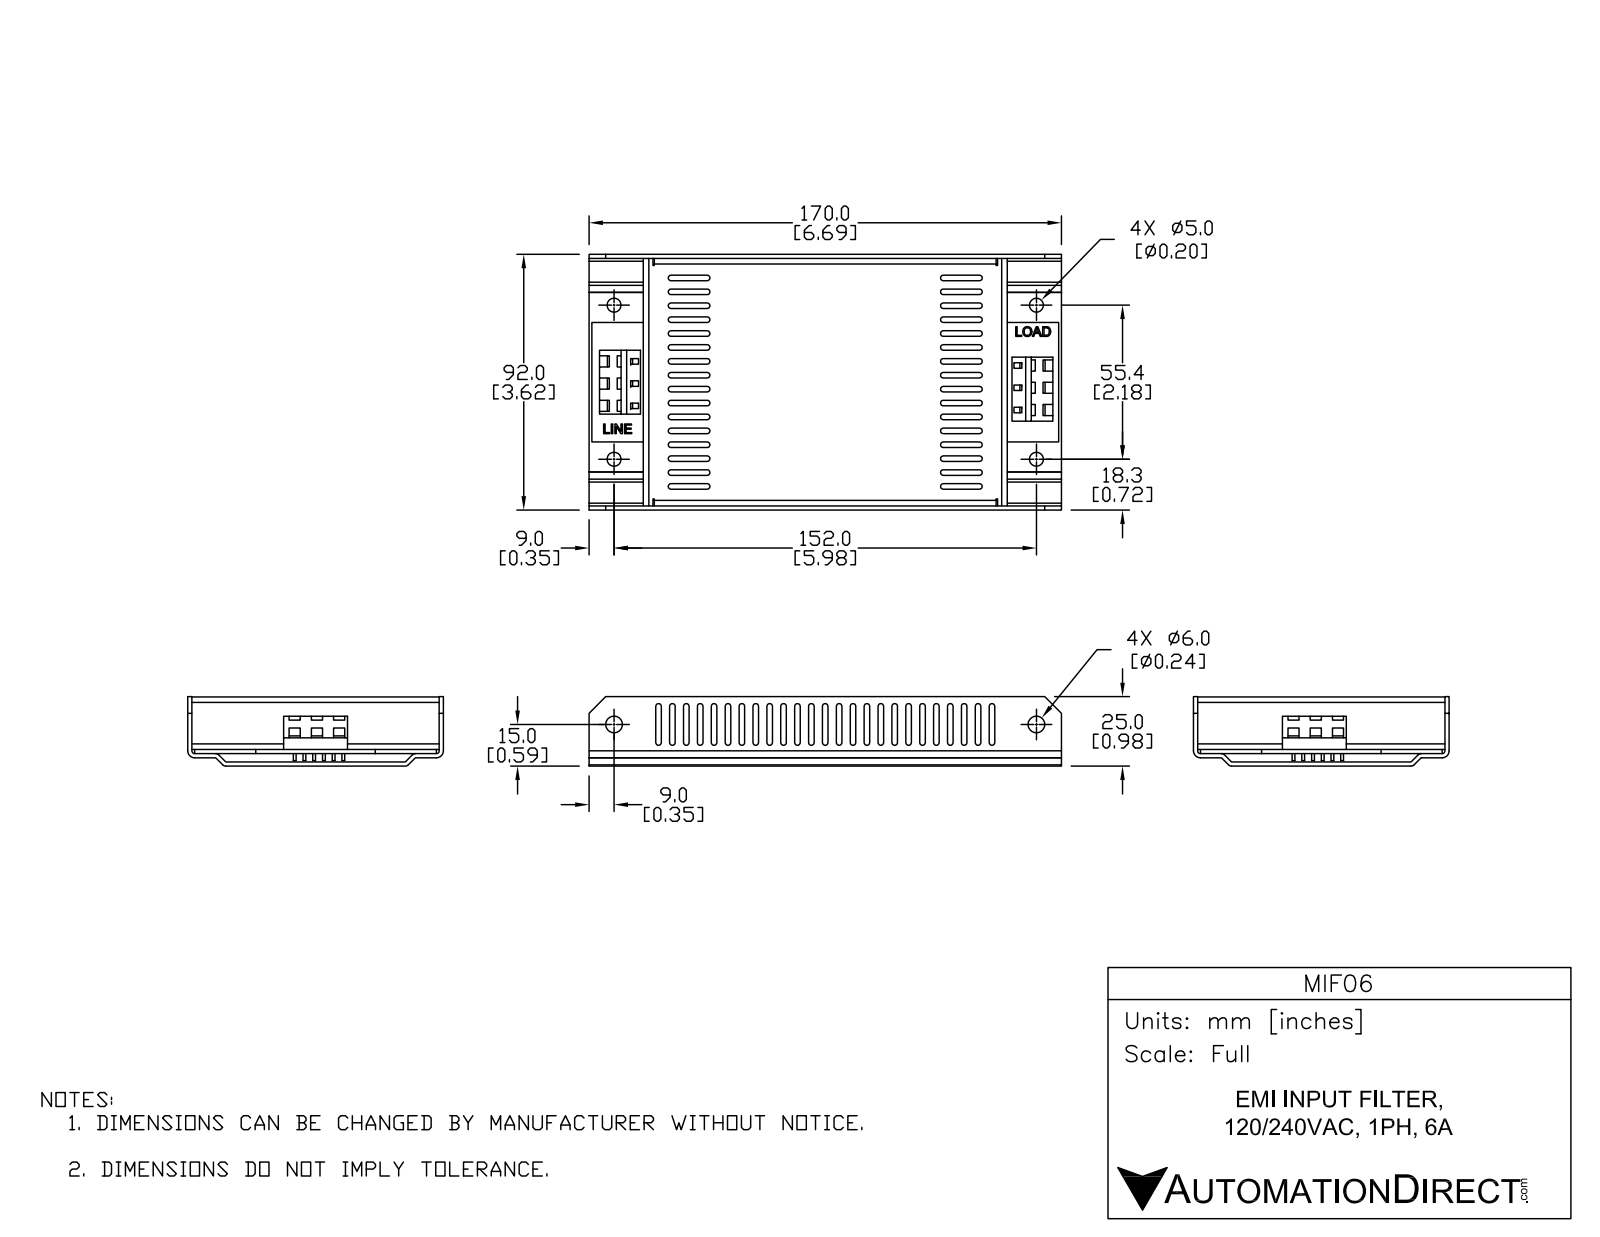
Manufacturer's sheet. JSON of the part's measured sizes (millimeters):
{"part_name": "MIF06", "step_written_by": "SolidWorks 2017 (AUTOMOTIVE_DESIGN)", "units": "millimeters", "bodies": {"solids": 5, "faces": 859, "planar": 451, "cylindrical": 349, "other": 59}, "overall_size": [170, 92, 25], "volume_mm3": 71530, "surface_area_mm2": 108700, "round_holes": [[1, 46], [3.3, 4], [3.5, 4], [4, 4], [5, 4], [6, 2]], "round_bosses_or_shafts": [[1, 10]], "partial_cylinders_radius": [[1, 122], [2, 6], [0.1, 4], [1.5, 4], [2.5, 2], [2.1, 1], [2.6, 1], [2.8, 1]], "face_to_face_distances": [1.5, 4.5, 3, 1, 6, 17.9, 24.9, 23.4, 20.4, 18.9], "hole_center_spacings": [17.7, 18.7, 68.8, 138, 153.1, 15.5, 20.3, 152]}
